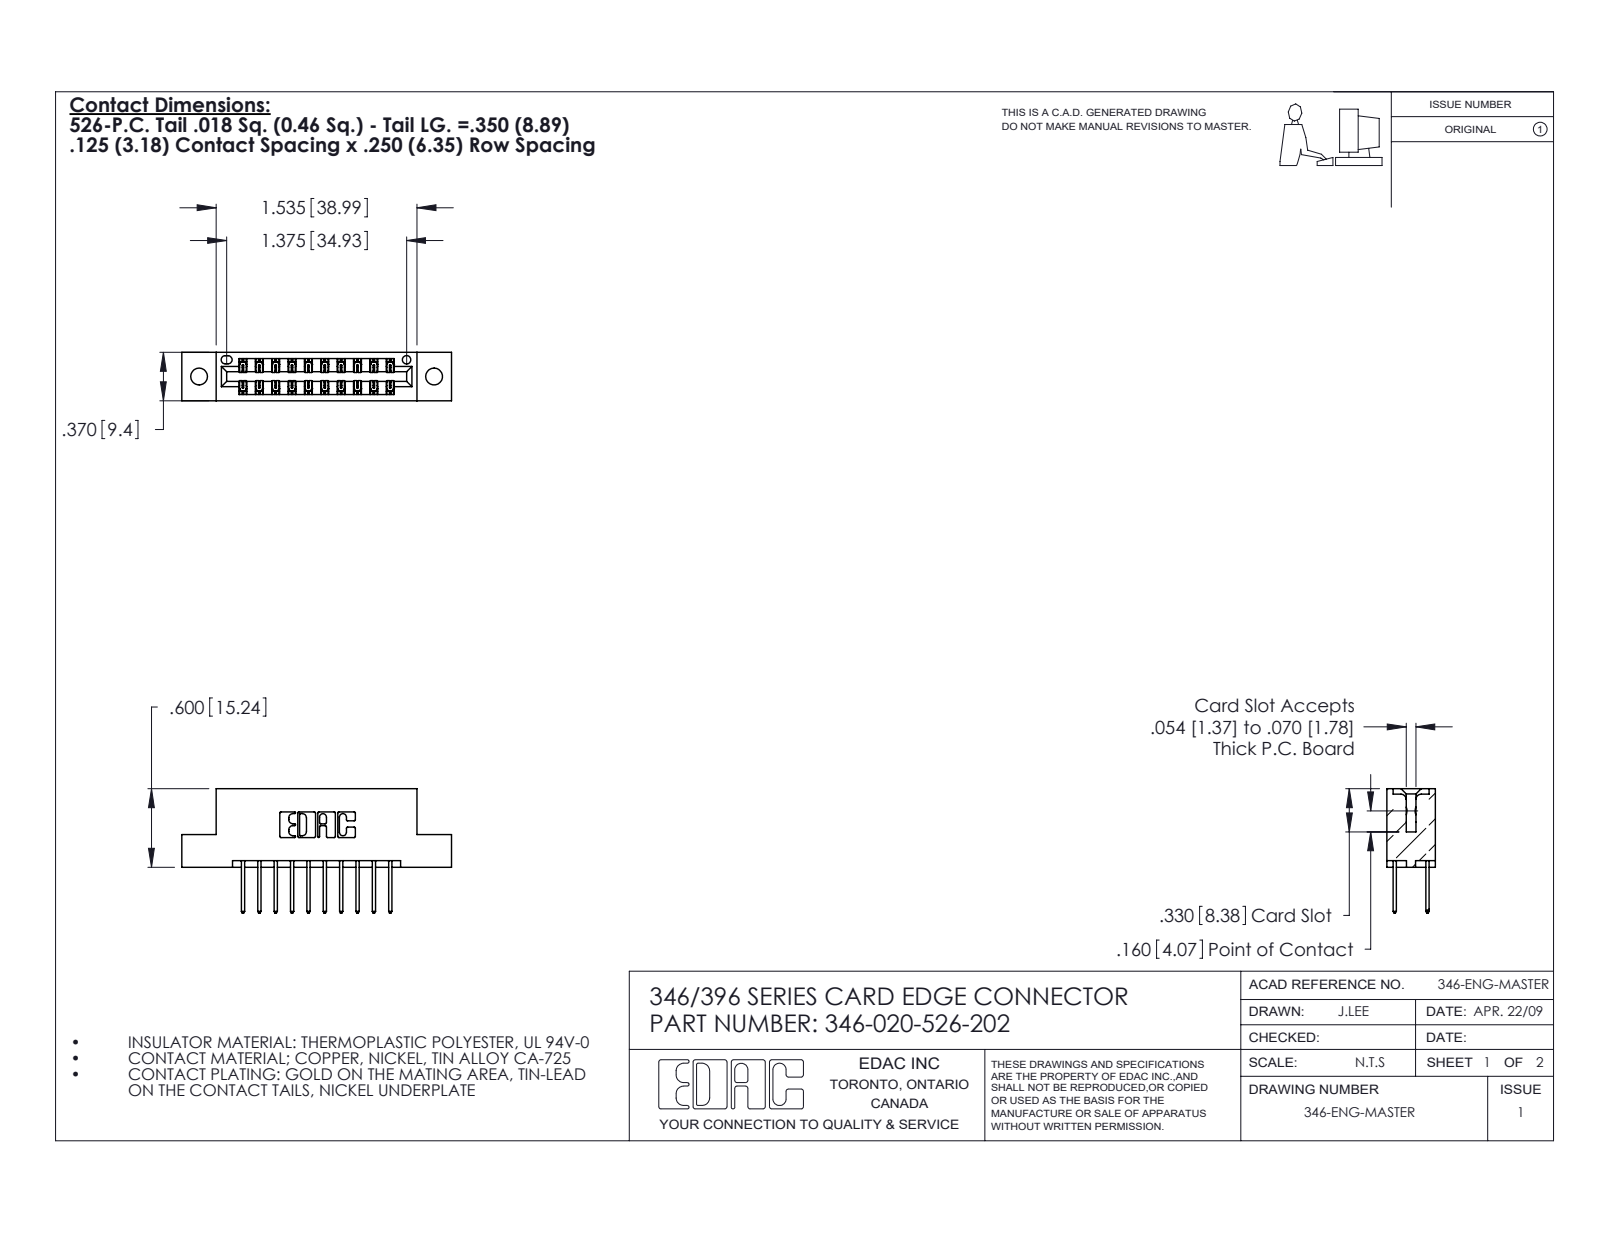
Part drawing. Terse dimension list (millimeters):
name: 345-292-001_345-293-126; 346-020-526-202; 346 Part_Flush Mounting Lugs - 0.128 Dia
written by: SolidWorks 2020 (CONFIG_CONTROL_DESIGN)
unit: mm
bodies: 21 solids, 1162 faces (776 planar, 386 cylindrical, 0 other)
size: 52.3 × 24.1 × 9.4
volume: 4 850 mm³; area: 6 041 mm²
holes: 2× ⌀3.3, 1× ⌀1.6
rounds: 30× R0.2, 22× R0.3, 20× R0.3, 6× R0.2, 6× R0.8, 3× R0.7, 2× R0.4, 2× R0.6
face distances: 6.4, 1.2, 8.2, 9.4, 1.8, 7.6, 0.6, 7, 3.8, 5.6
hole spacings: 6.2, 40.4, 45.6
